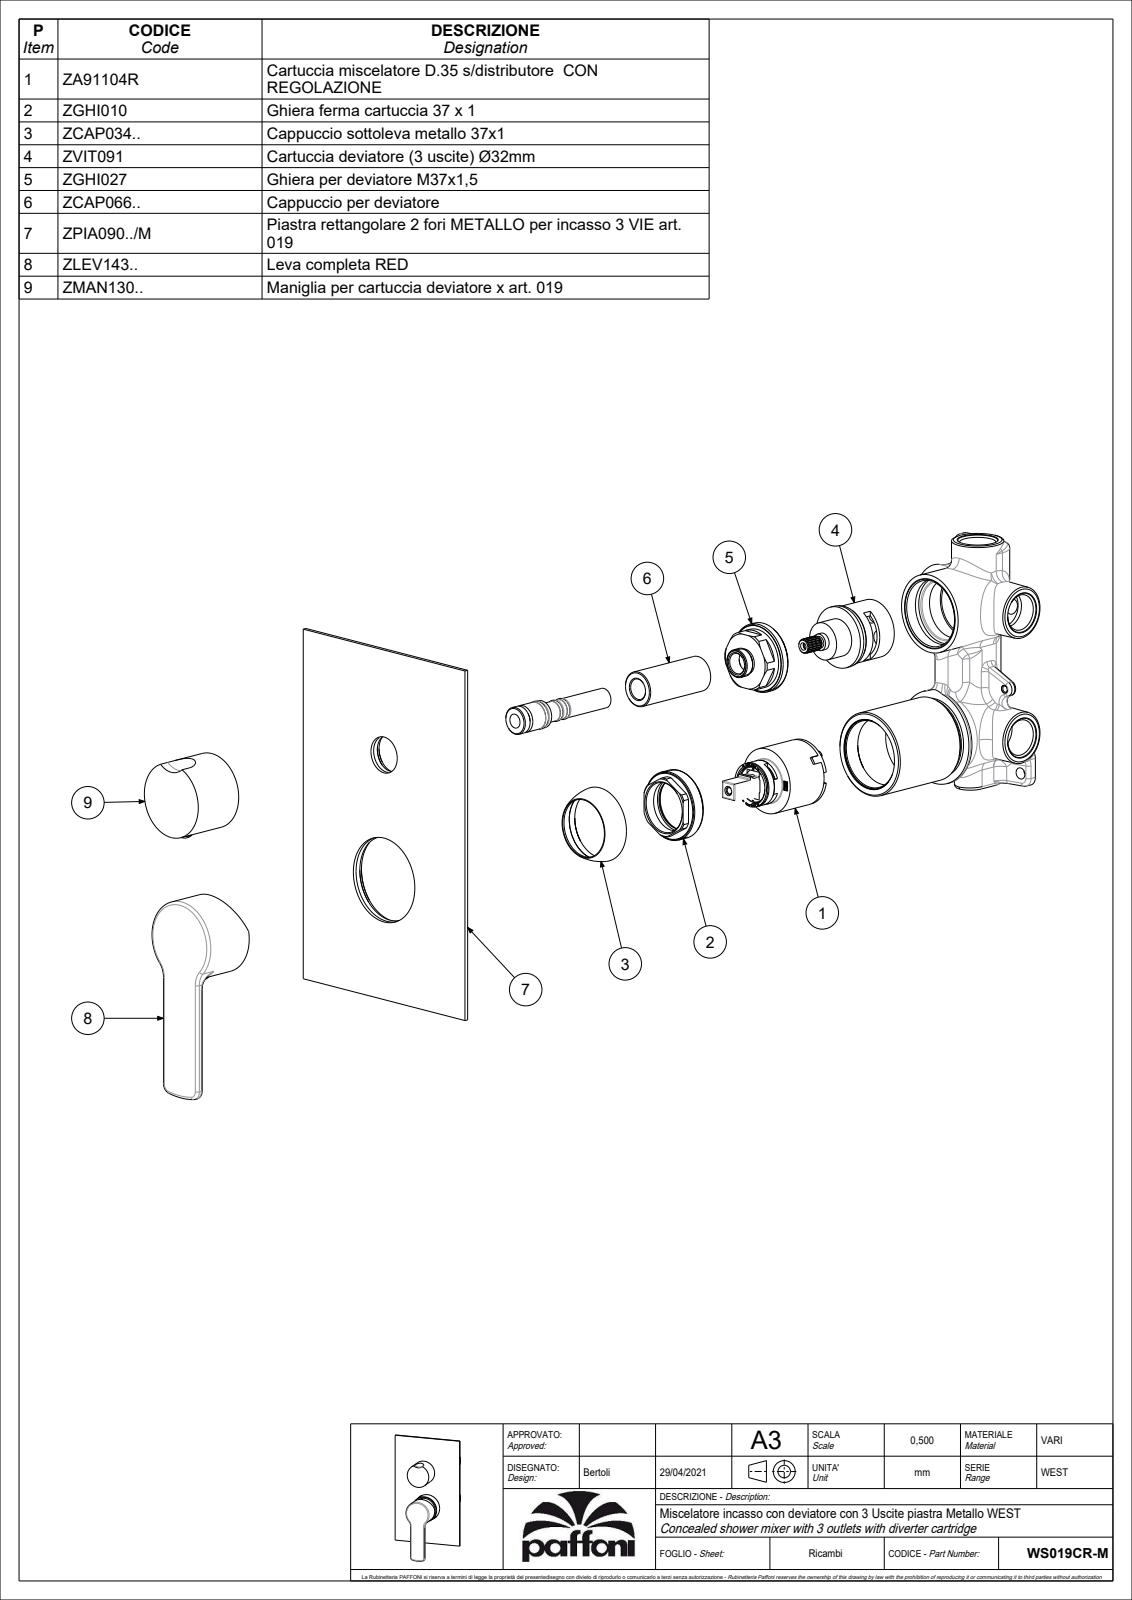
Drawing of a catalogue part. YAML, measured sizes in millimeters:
part_name: "WS018CR-M"
step_written_by: "CREO PARAMETRIC BY PTC INC, 2020044 (CONFIG_CONTROL_DESIGN)"
units: millimeters
bodies: {solids: 4, faces: 1089, planar: 590, cylindrical: 283, other: 216}
overall_size: [210, 120, 57.1]
volume: 121532
surface_area: 93459
round_holes:
  - {diameter: 3, count: 2}
  - {diameter: 4, count: 2}
  - {diameter: 4.5, count: 2}
  - {diameter: 19.5, count: 2}
  - {diameter: 36, count: 2}
  - {diameter: 3.2, count: 1}
  - {diameter: 3.3, count: 1}
  - {diameter: 4.2, count: 1}
  - {diameter: 5, count: 1}
  - {diameter: 11, count: 1}
  - {diameter: 14.8, count: 1}
  - {diameter: 19.9, count: 1}
round_bosses_or_shafts:
  - {diameter: 7.6, count: 2}
  - {diameter: 5.5, count: 2}
  - {diameter: 44.8, count: 1}
  - {diameter: 43, count: 1}
  - {diameter: 40, count: 1}
  - {diameter: 35, count: 1}
  - {diameter: 24, count: 1}
  - {diameter: 23.5, count: 1}
partial_cylinders:
  - {radius: 0.5, count: 45}
  - {radius: 0.15, count: 11}
  - {radius: 0.3, count: 4}
  - {radius: 1.5, count: 4}
  - {radius: 1, count: 2}
  - {radius: 5, count: 2}
  - {radius: 10, count: 2}
  - {radius: 7, count: 1}
face_to_face_distances: [2, 57.1, 55.1, 4.5, 52.6, 50.6, 9, 13, 15, 5.5]
hole_center_spacings: [2.3, 10, 12.5, 14.8, 68, 78]
